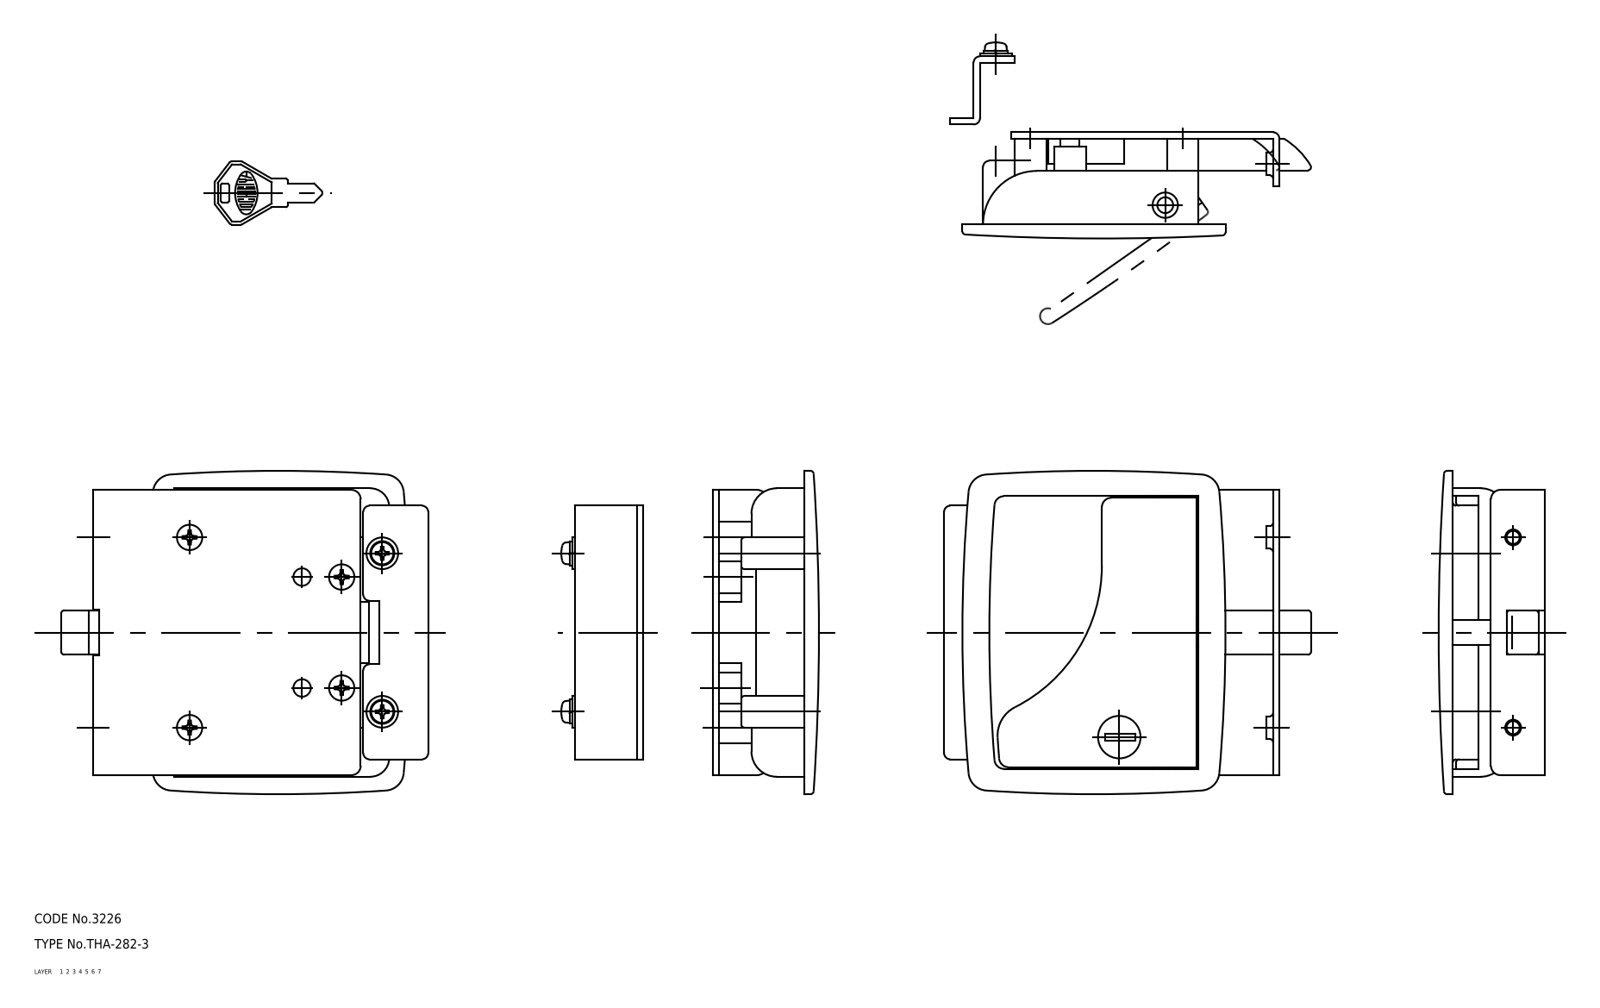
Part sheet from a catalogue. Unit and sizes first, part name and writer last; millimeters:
Units: millimetres
Overall size (bounding box): 114.5 × 102 × 95.54
Volume: 94 765 mm³ · Surface area: 74 582 mm²
Bodies: 9 solids, 583 faces (0 planar, 0 cylindrical, 583 other)
Part name (STEP PRODUCT): bracket_B_mr; handle_mr; lock_mr; screw_mr (+5 more)
STEP written by: CADfix (AUTOMOTIVE_DESIGN)
